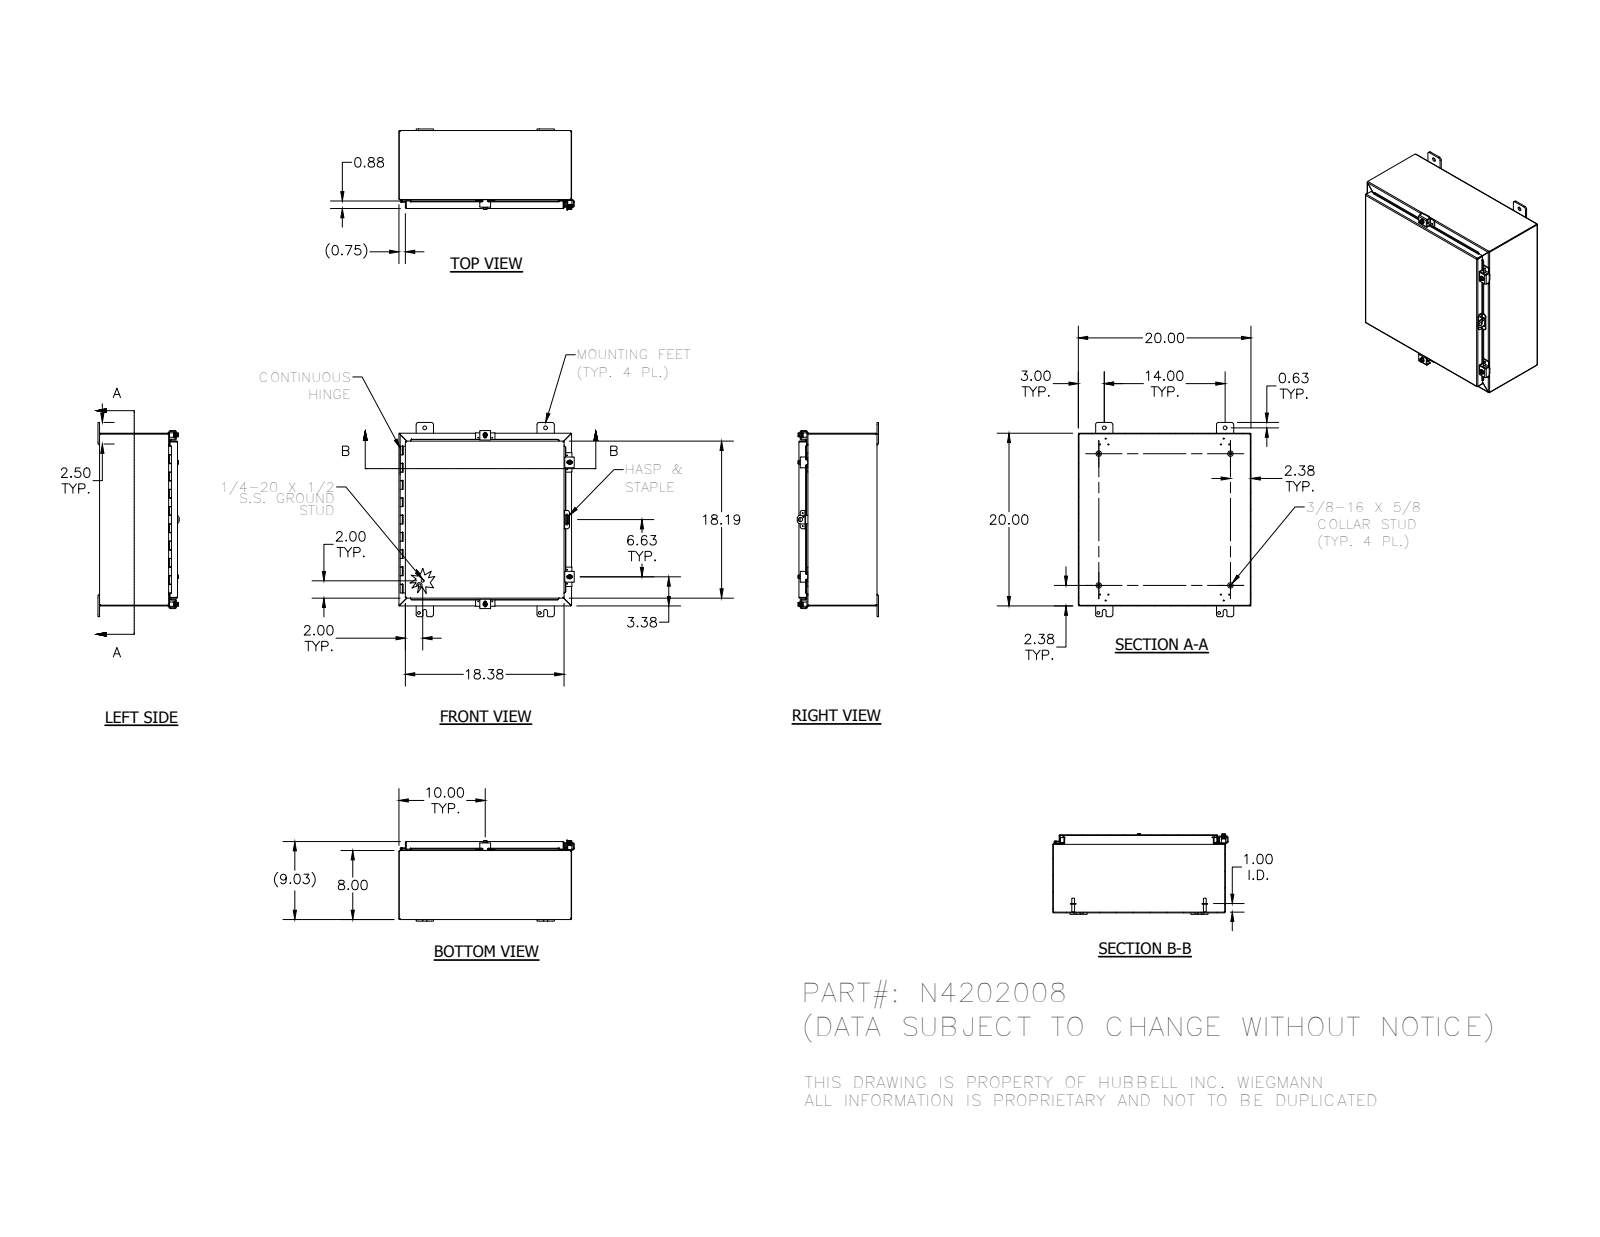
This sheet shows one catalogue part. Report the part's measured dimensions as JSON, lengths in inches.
{"part_name": "328104L_1; 328104T_1; N42020LID_1; 38846_1 (+8 more)", "step_written_by": "SolidWorks 2014 (AUTOMOTIVE_DESIGN)", "units": "inches", "bodies": {"solids": 37, "faces": 1614, "planar": 633, "cylindrical": 724, "other": 257}, "overall_size": [22.5, 20.311, 9.41], "volume_in3": 134.2, "surface_area_in2": 3489, "round_holes": [[0.12, 12], [0.11, 11], [0.211, 4], [0.281, 4], [0.3, 4], [0.313, 4], [0.438, 4], [0.125, 1], [0.156, 1], [0.5, 1]], "round_bosses_or_shafts": [[0.25, 6], [0.625, 4], [0.52, 4], [0.5, 4], [0.35, 4], [0.33, 4], [0.115, 2], [0.337, 1]], "partial_cylinders_radius": [[0.03, 49], [0.062, 33], [0.125, 33], [0.25, 29], [0.031, 23], [0.105, 23], [0.07, 8], [0.141, 8]], "face_to_face_distances": [0.074, 8.959, 19.926, 8.885, 9.033, 19.852, 20, 7.926, 1.033, 8], "hole_center_spacings": [14, 0.876, 0.759, 0.839, 0.94, 0.969, 1.593, 1.995]}
